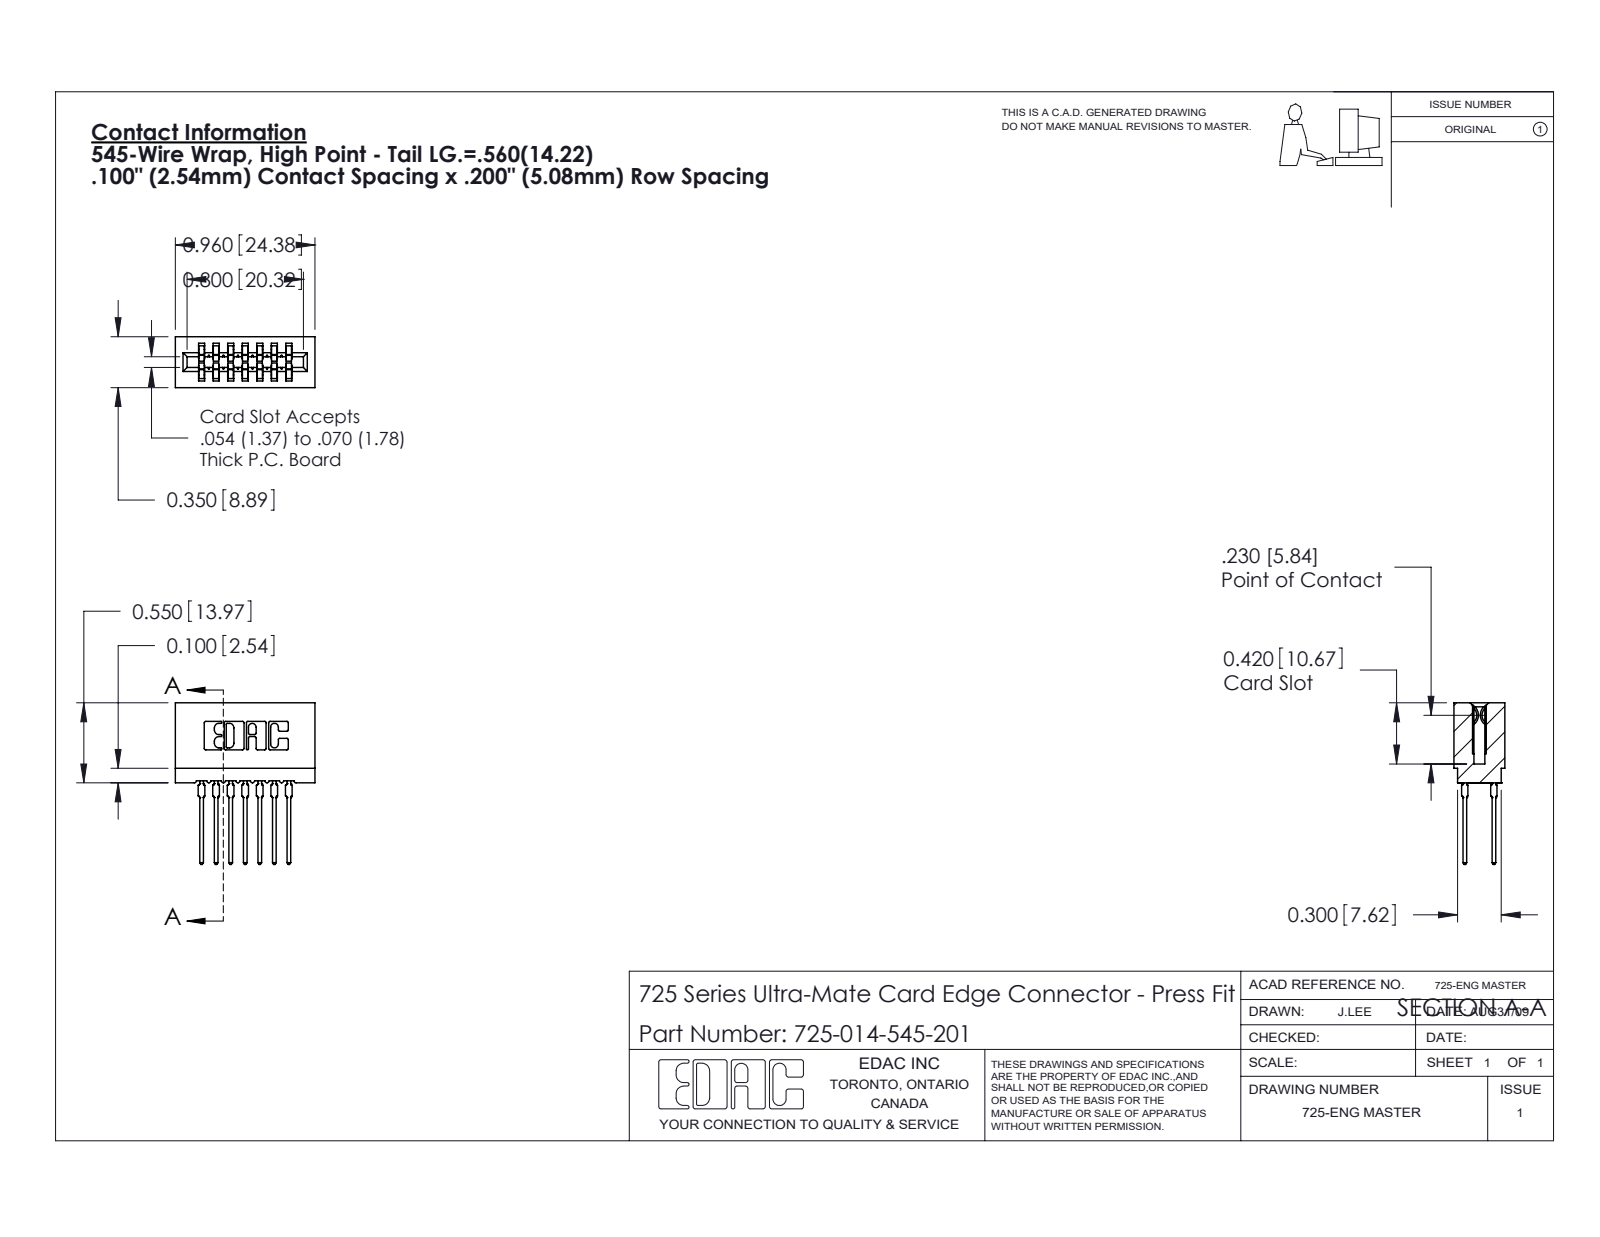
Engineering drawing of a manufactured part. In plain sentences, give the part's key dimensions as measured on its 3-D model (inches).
The part is named "725-014-545-201; 725 Part_Insulator Option - 01; 745-292-001_545". Its 3-D file was written by "SolidWorks 2020 (CONFIG_CONTROL_DESIGN)". It is 15 solids with 1348 faces: 699 planar, 285 cylindrical and 364 other. Overall it measures 1.111 by 0.96 by 0.35 inches. Its volume is 0.132 cubic inches and its surface area 6.24 square inches. Partial cylindrical surfaces (rounded edges, fillets, slot ends): 28 of radius 0.021, 22 of radius 0.01, 14 of radius 0.015, 8 of radius 0.005, 8 of radius 0.011, 6 of radius 0.007, 6 of radius 0.031, 3 of radius 0.026. The main face-to-face distances are 0.2, 0.1, 0.3, 0.042, 0.4, 0.142, 0.058, 0.063, 0.287, 0.242.
